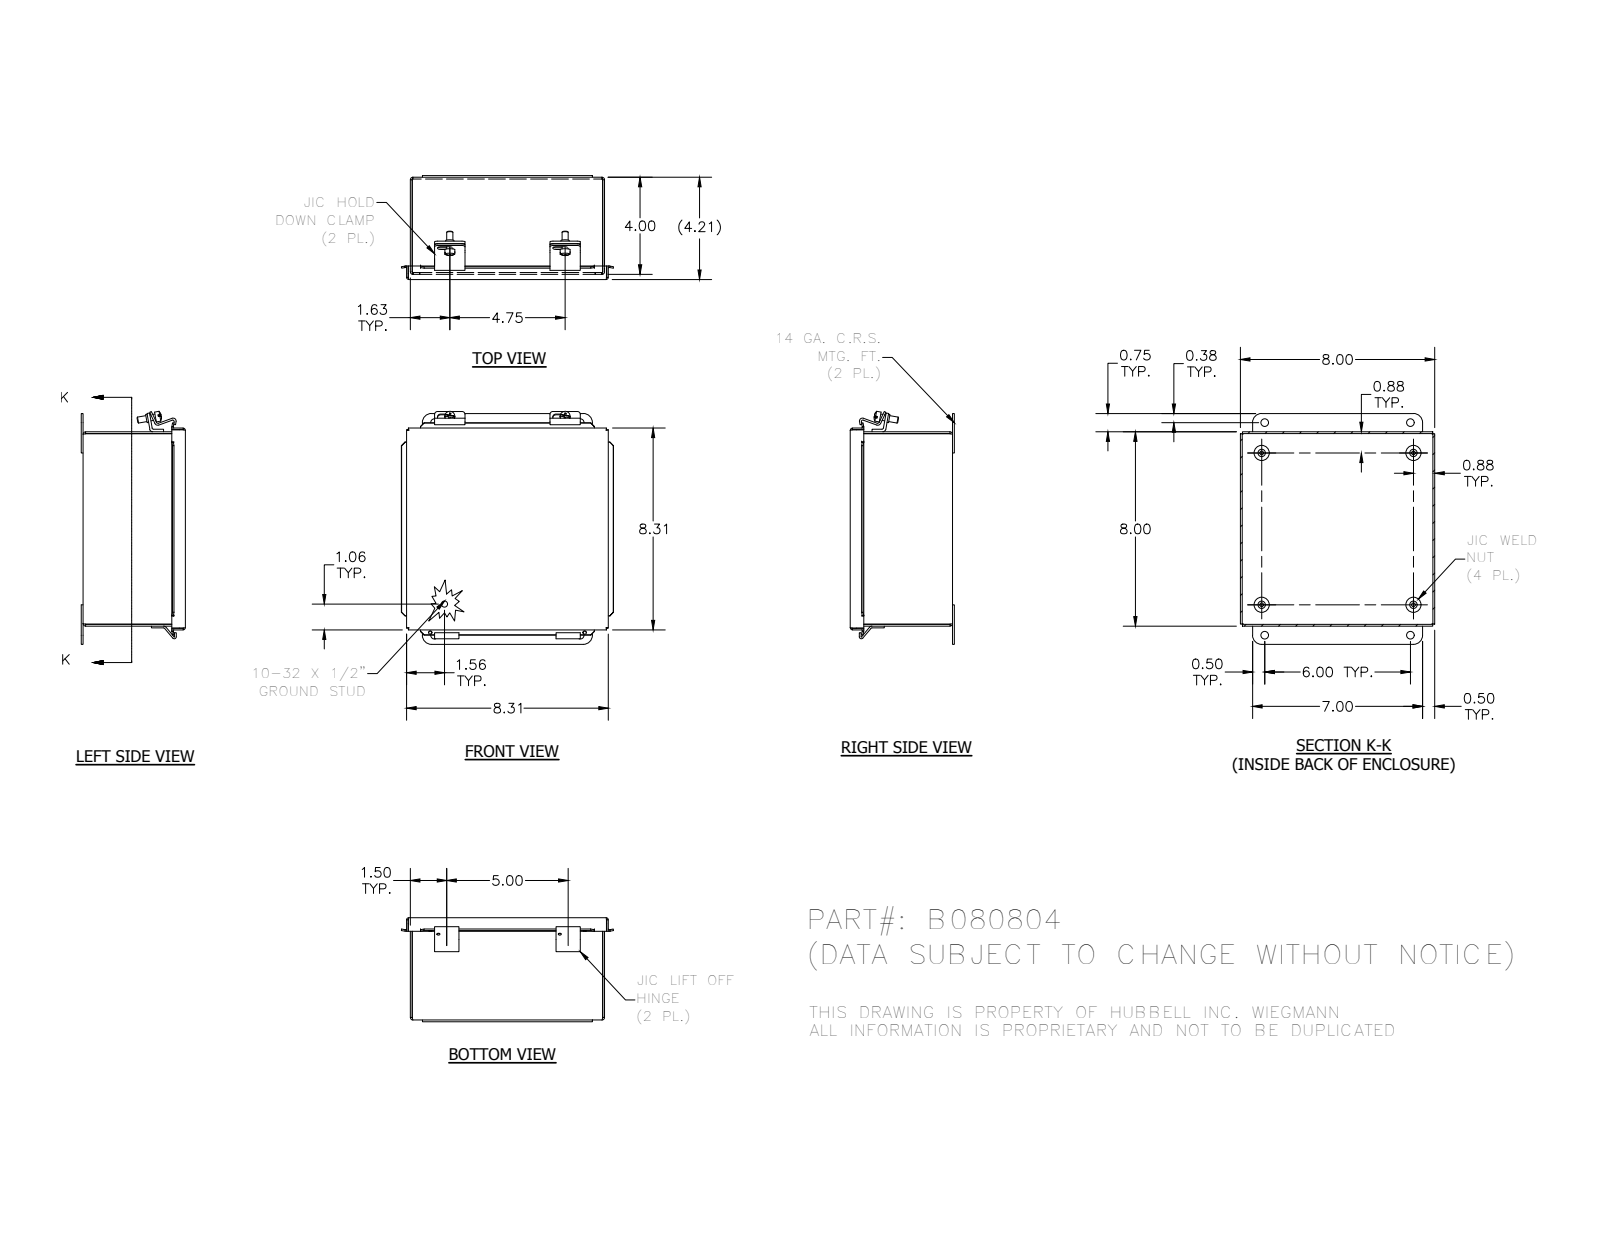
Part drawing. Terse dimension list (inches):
name: B080804; 3499; 3483; C1001 (+7 more)
written by: Autodesk Inventor 2012 (AUTOMOTIVE_DESIGN)
unit: in
bodies: 19 solids, 422 faces (279 planar, 98 cylindrical, 45 other)
size: 9.593 × 8.739 × 4.287
volume: 26.3 in³; area: 702.4 in²
holes: 4× ⌀0.156, 4× ⌀0.31, 2× ⌀0.125, 2× ⌀0.14, 2× ⌀0.196
bosses: 4× ⌀0.625, 4× ⌀0.3, 3× ⌀0.25, 2× ⌀0.41, 2× ⌀0.344, 1× ⌀0.19
rounds: 16× R0.031, 8× R0.093, 8× R0.105, 8× R0.125, 4× R0.133, 4× R0.375, 3× R0.063, 3× R0.126
face distances: 0.074, 7.926, 4.15, 4.212, 0.062, 4.076, 4.138, 8, 7.852, 0.075
hole spacings: 1.257, 7.501, 6, 6.25, 6.25, 6.251, 6.252, 8.839
